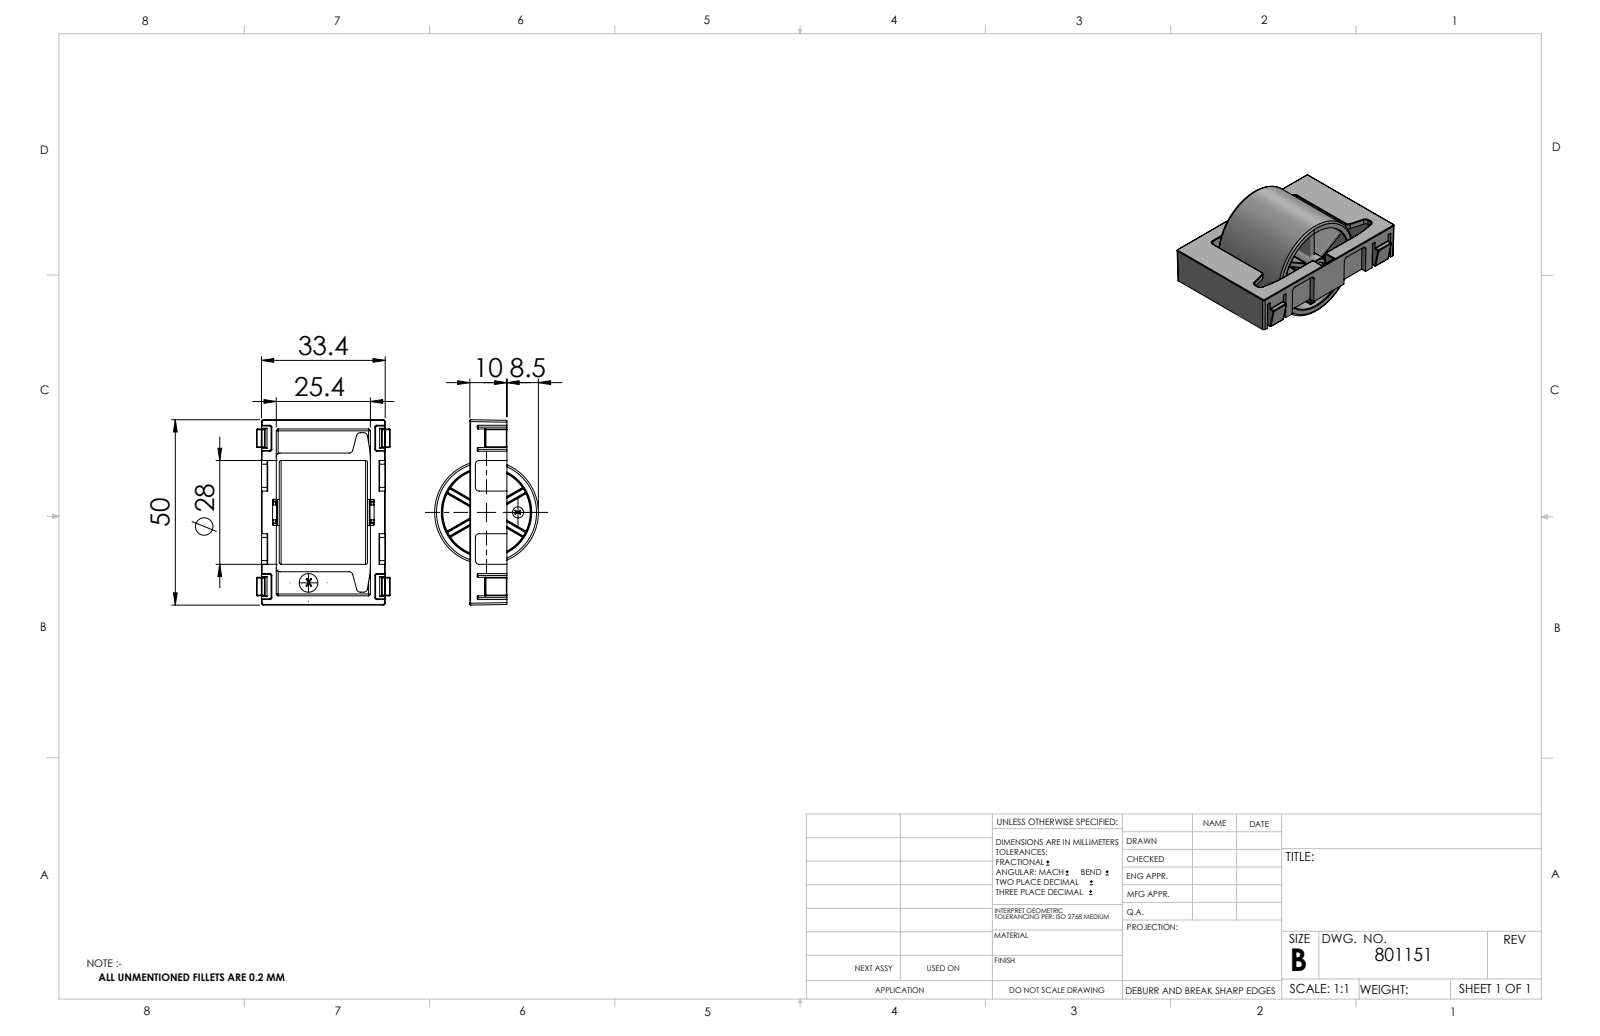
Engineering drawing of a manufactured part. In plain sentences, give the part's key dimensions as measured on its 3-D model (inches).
The part is named "801151_c_1". Its 3-D file was written by "SolidWorks 2014 (CONFIG_CONTROL_DESIGN)". It is 3 solids with 744 faces: 172 planar, 290 cylindrical and 282 other. Overall it measures 1.968 by 1.413 by 1.102 inches. Its volume is 0.689 cubic inches and its surface area 20.48 square inches. Round holes: 1 of diameter 0.165, 1 of diameter 0.945. Round bosses or shafts: 1 of diameter 1.102, 1 of diameter 0.276, 1 of diameter 0.198, 1 of diameter 0.157, 1 of diameter 0.118. Partial cylindrical surfaces (rounded edges, fillets, slot ends): 144 of radius 0.008, 22 of radius 0.02, 12 of radius 0.039, 2 of radius 0.004, 2 of radius 0.787, 1 of radius 0.081. The main face-to-face distances are 0.059, 0.484, 0.516, 0.031, 0.394, 0.856, 0.915, 1, 0.079, 0.335.
